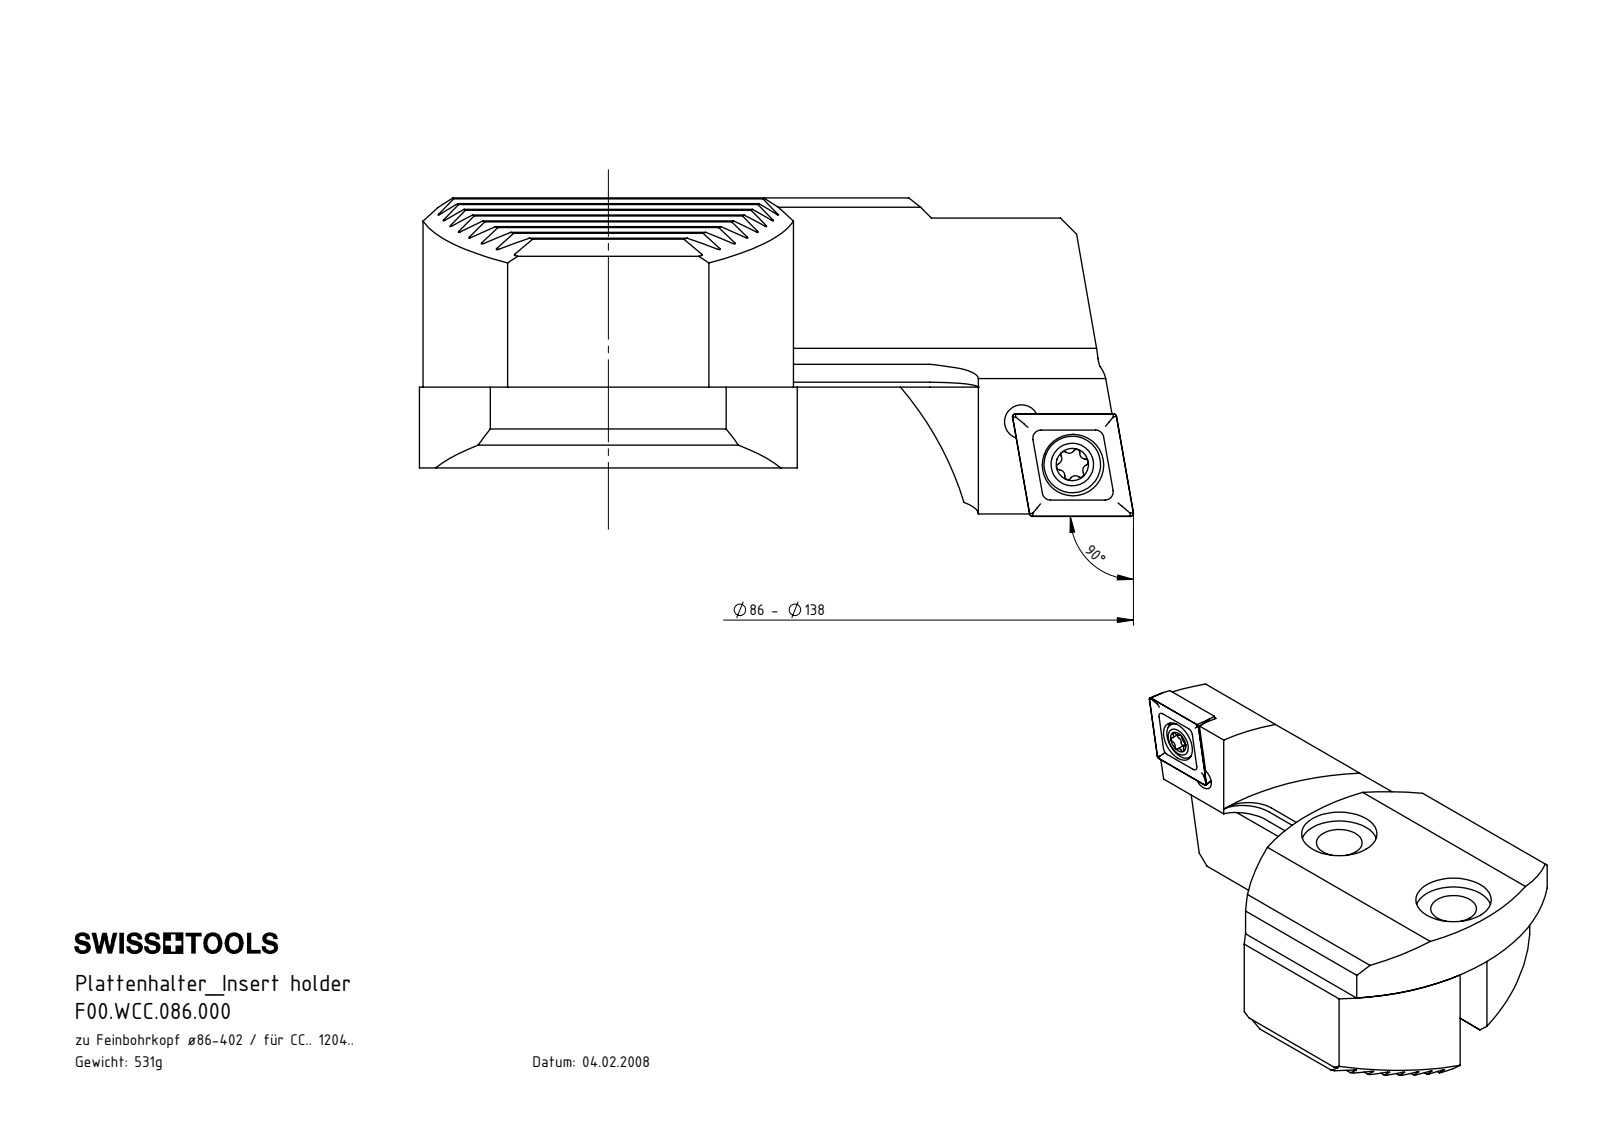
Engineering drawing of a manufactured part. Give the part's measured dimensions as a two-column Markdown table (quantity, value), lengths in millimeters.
| quantity | value |
| --- | --- |
| part name | F00.WCC.086.000; F00-WCB.086.003_A; F00-WCC.086.001_C; CCMT120404 (+3 more) |
| STEP written by | SolidWorks 2017 (AUTOMOTIVE_DESIGN) |
| units | millimeters |
| bodies | 5 solids, 439 faces (264 planar, 60 cylindrical, 115 other) |
| overall size | 88.38 × 55 × 39.4 |
| volume | 67 589 mm³ |
| surface area | 19 711 mm² |
| round holes (diameter × count) | 4.2 × 2, 8.5 × 2, 14 × 2, 5.5 × 1, 7.6 × 1 |
| round bosses / shafts (diameter × count) | 7 × 1, 5 × 1 |
| partial cylindrical surfaces (radius × count) | 0.2 × 16, 40 × 7, 0.39 × 6, 0.69 × 6, 0.8 × 1, 6 × 1 |
| main face-to-face distances | 2.38, 4.76, 21.3, 33.7, 12.4, 7.14, 10, 9.52, 4.77, 7.15 |
| hole center spacings | 8.21, 8.33, 30 |
